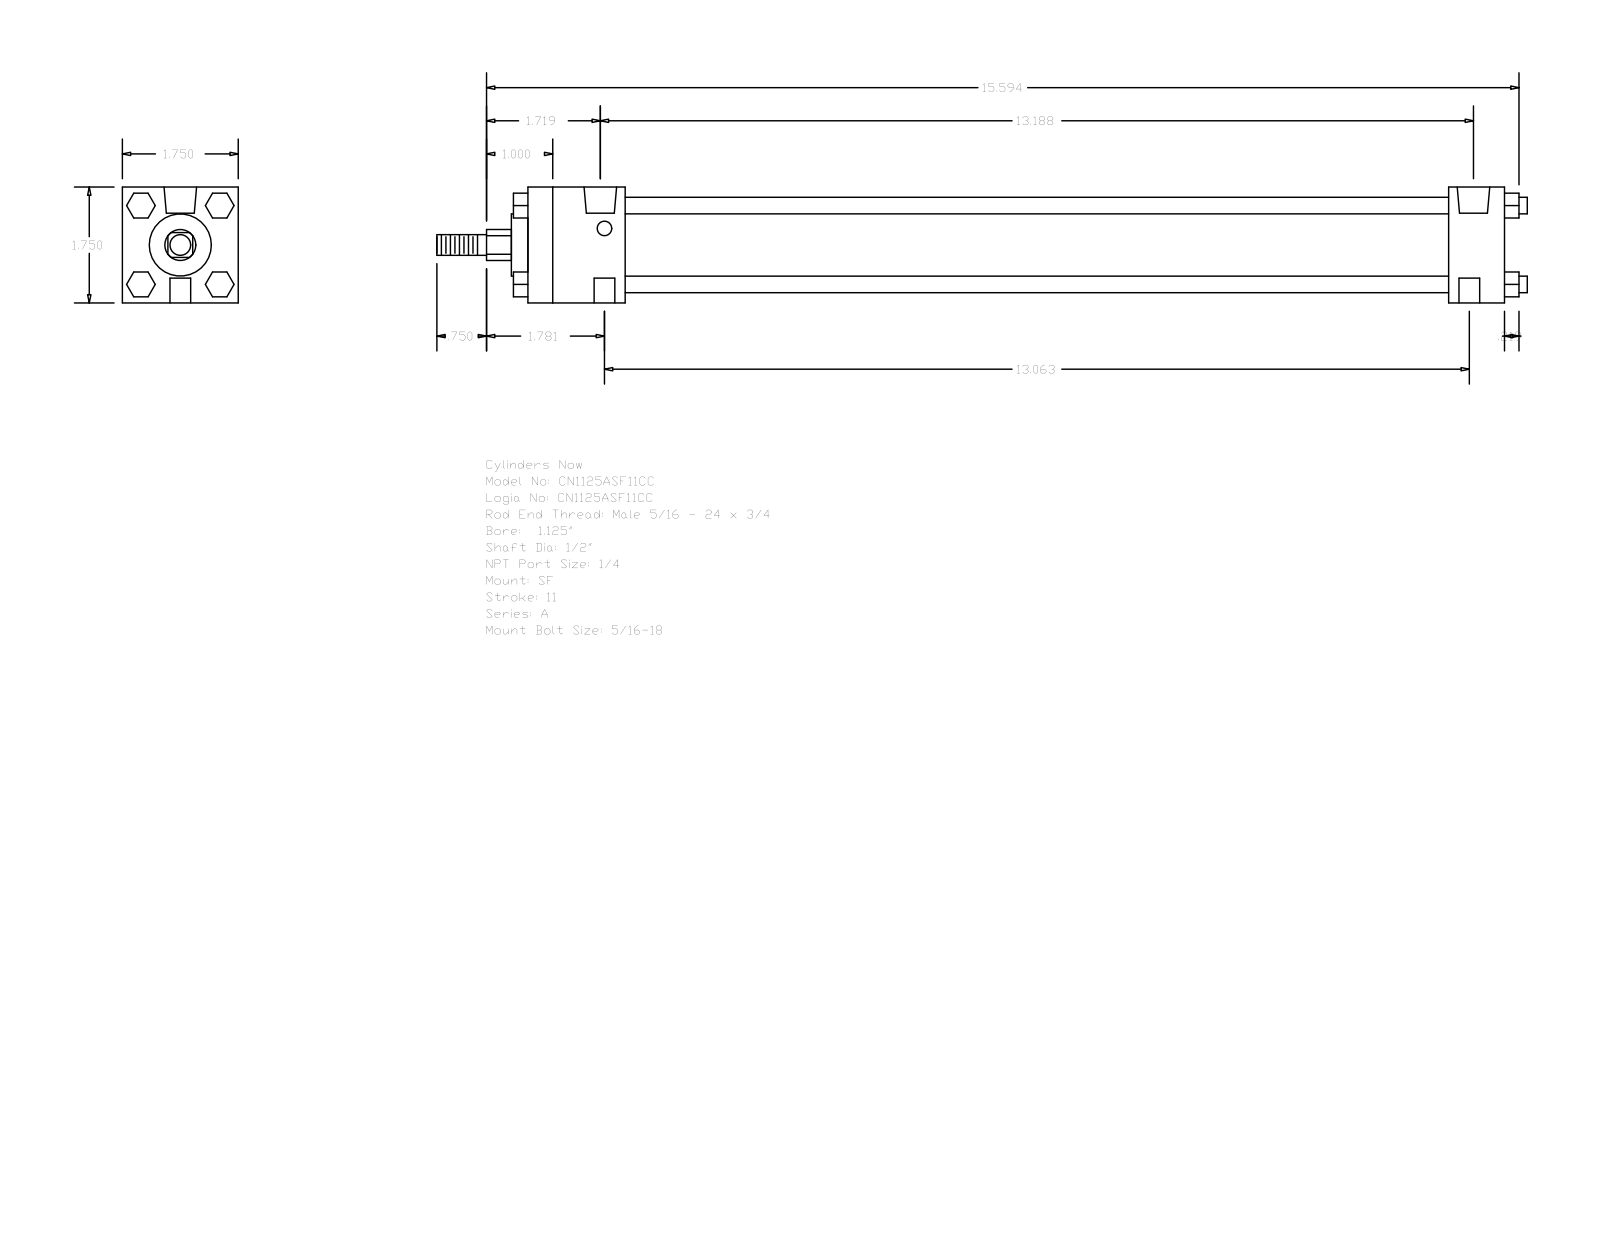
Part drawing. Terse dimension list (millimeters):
name: A_SF__0112_0.5
written by: GSSL Pune (CONFIG_CONTROL_DESIGN)
unit: mm
bodies: 0 solids, 120 faces (92 planar, 28 cylindrical, 0 other)
size: 418.31 × 44.45 × 44.45
holes: 2× ⌀5.56, 2× ⌀7.94, 2× ⌀12.49
bosses: 4× ⌀6.35, 1× ⌀31.88, 1× ⌀23.81, 1× ⌀12.7, 1× ⌀7.94
rounds: 1× R5.94
face distances: 44.46, 374.64, 353.21, 21.43, 37.3, 315.91, 337.34, 9.53, 5.59, 5.56
hole spacings: 331.79, 1.58, 1.59, 333.37, 333.38, 334.96
